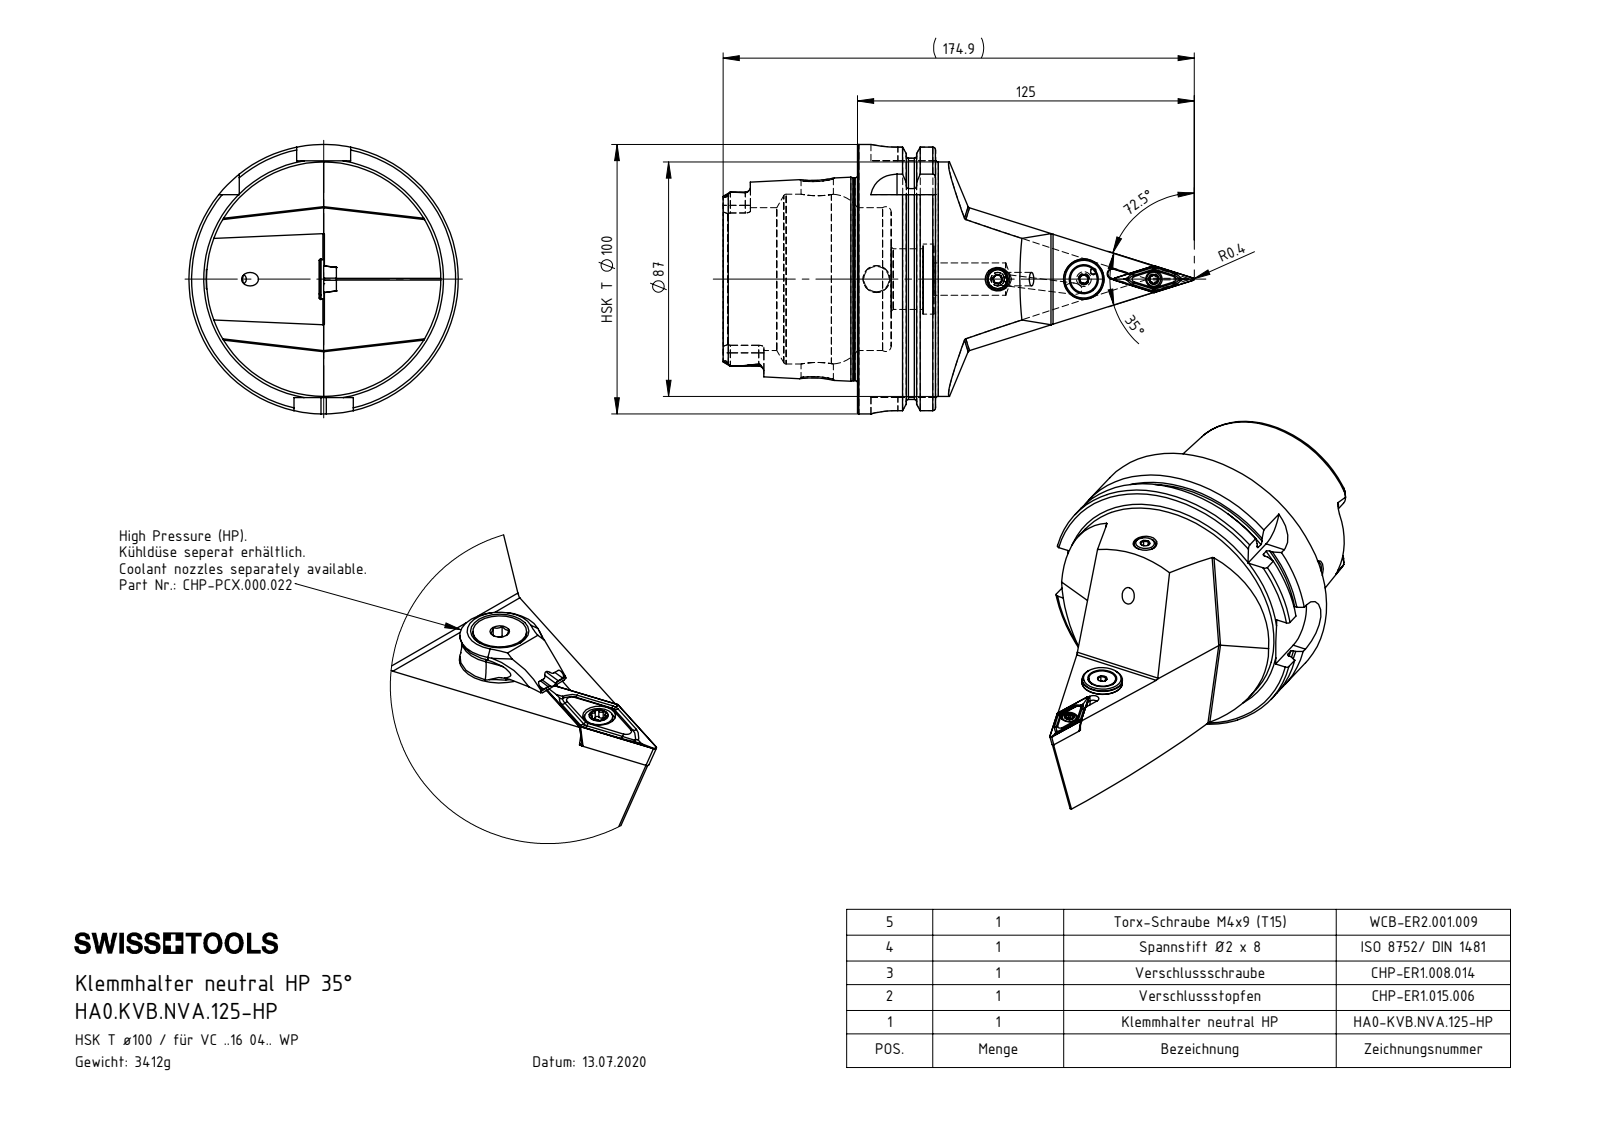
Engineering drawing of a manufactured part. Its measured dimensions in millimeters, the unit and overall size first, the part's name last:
Units: millimetres
Overall size (bounding box): 174.88 × 100 × 100
Round holes (diameter × count): ⌀4.2 ×2, ⌀5 ×2, ⌀12 ×2, ⌀1.2 ×1, ⌀2 ×1, ⌀2.5 ×1, ⌀3 ×1, ⌀3.3 ×1, ⌀4.4 ×1, ⌀5.2 ×1, ⌀6.1 ×1, ⌀7 ×1
Round bosses / shafts (diameter × count): ⌀100 ×1, ⌀91.95 ×1, ⌀87 ×1, ⌀75.26 ×1, ⌀15 ×1, ⌀13.4 ×1, ⌀10 ×1, ⌀8 ×1
Partial cylindrical surfaces — rounded edges, fillets, slot ends (radius × count): R0.34 ×6, R0.59 ×6, R1.9 ×6, R0.8 ×5, R4.88 ×4, R10 ×4, R1.75 ×1
Main face-to-face distances: 12.45, 28.95, 16.5, 49.9, 62.35, 78.85, 87.8, 28.3, 78.2, 15.85
Hole centre spacings: 4.5, 22.64, 22.76, 25.96, 26.08, 32, 35.61, 45
Volume: 433 886 mm³ · Surface area: 66 957 mm²
Bodies: 8 solids, 308 faces (117 planar, 76 cylindrical, 115 other)
Part name (STEP PRODUCT): ISO 8752 2x8; HA0.KVB.NVA.125-HP; WCB-ER2.001.009_A; CHP-ER1.015.006 (+6 more)
STEP written by: SolidWorks 2017 (AUTOMOTIVE_DESIGN)
